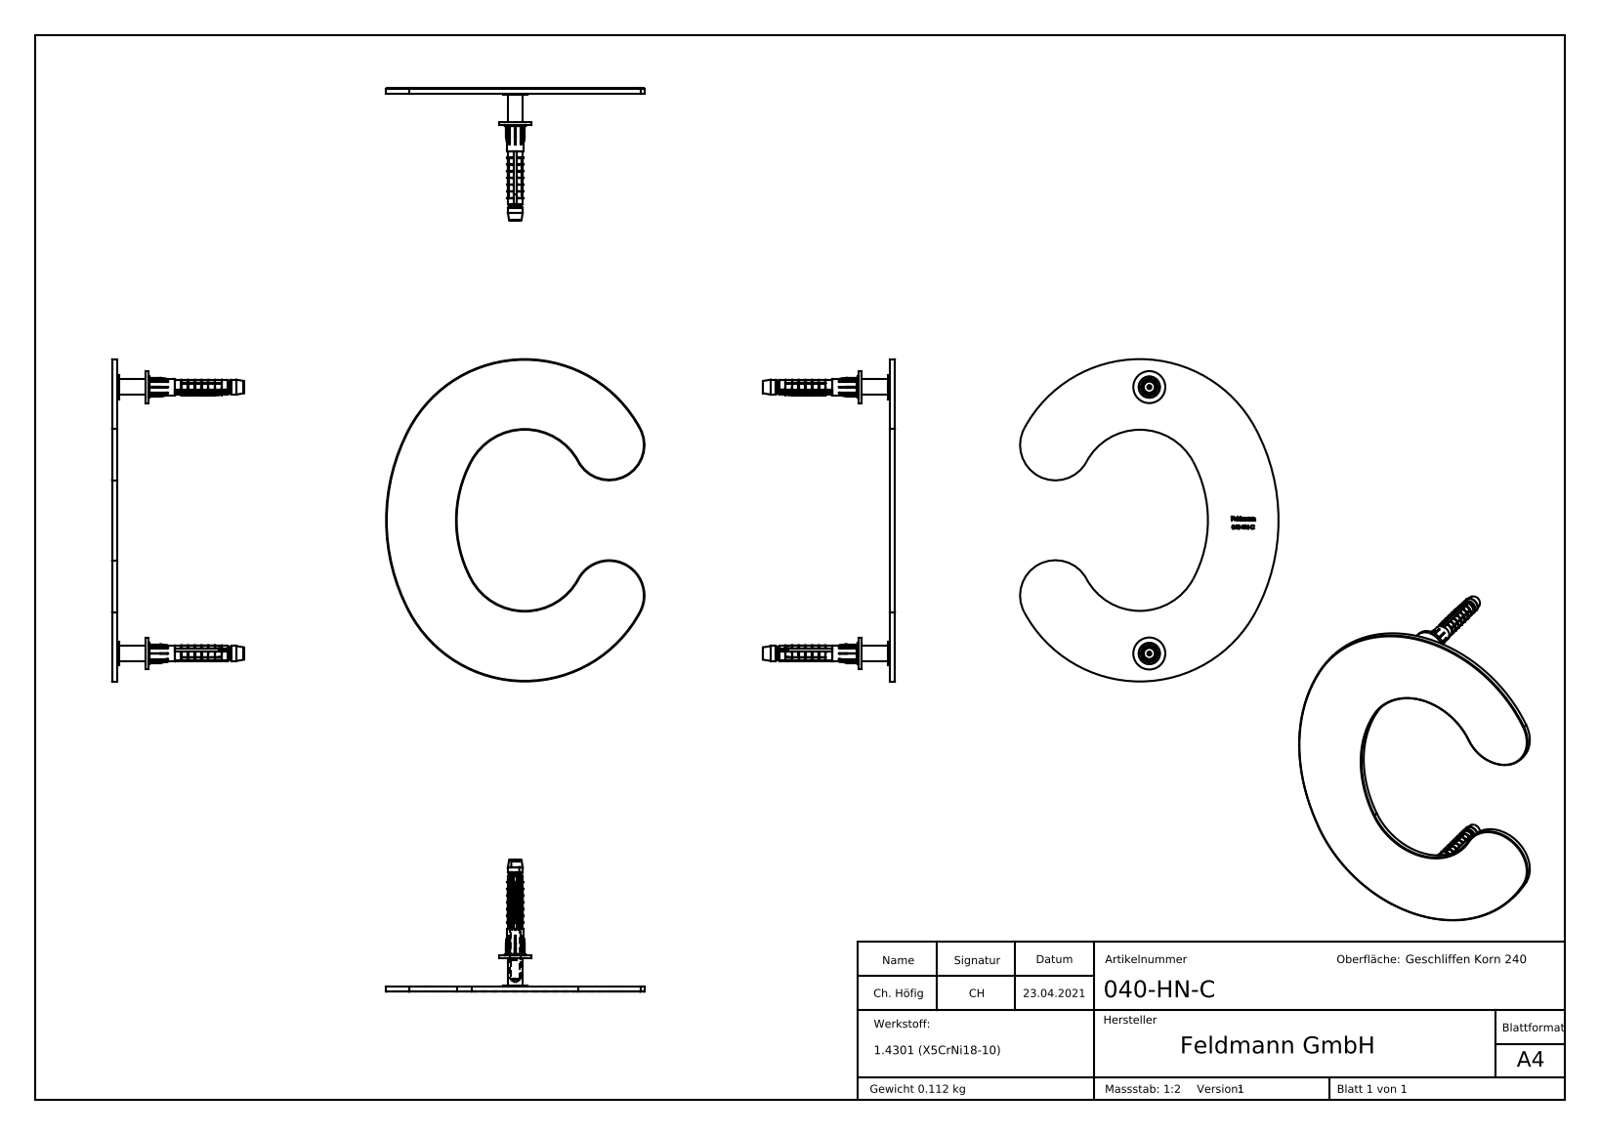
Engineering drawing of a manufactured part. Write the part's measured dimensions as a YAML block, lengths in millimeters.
part_name: "040-HN-X Teil4_040-HN-X Teil4; 040-HN-X Teil3; 040-HN-C; 040-HN-X Teil4 (+5 more)"
step_written_by: "SolidWorks 2018 (CONFIG_CONTROL_DESIGN)"
units: millimeters
bodies: {solids: 7, faces: 1552, planar: 353, cylindrical: 388, other: 811}
overall_size: [10000, 5217.43, 4607.88]
volume: 15131
surface_area: 17833
round_holes:
  - {diameter: 3.3, count: 2}
  - {diameter: 4.3, count: 2}
round_bosses_or_shafts:
  - {diameter: 12, count: 2}
  - {diameter: 9, count: 2}
  - {diameter: 8, count: 2}
  - {diameter: 6, count: 2}
  - {diameter: 5.8, count: 2}
  - {diameter: 5.6, count: 2}
  - {diameter: 4.6, count: 2}
  - {diameter: 4, count: 2}
partial_cylinders:
  - {radius: 0.1, count: 22}
  - {radius: 3.5, count: 2}
  - {radius: 13.25, count: 2}
  - {radius: 22.71, count: 2}
  - {radius: 49.21, count: 2}
  - {radius: 46.65, count: 1}
  - {radius: 73.15, count: 1}
face_to_face_distances: [2, 11.6, 13.6, 1.1, 10.5, 12.5, 1, 0.5, 2.5, 10]
hole_center_spacings: [100]
